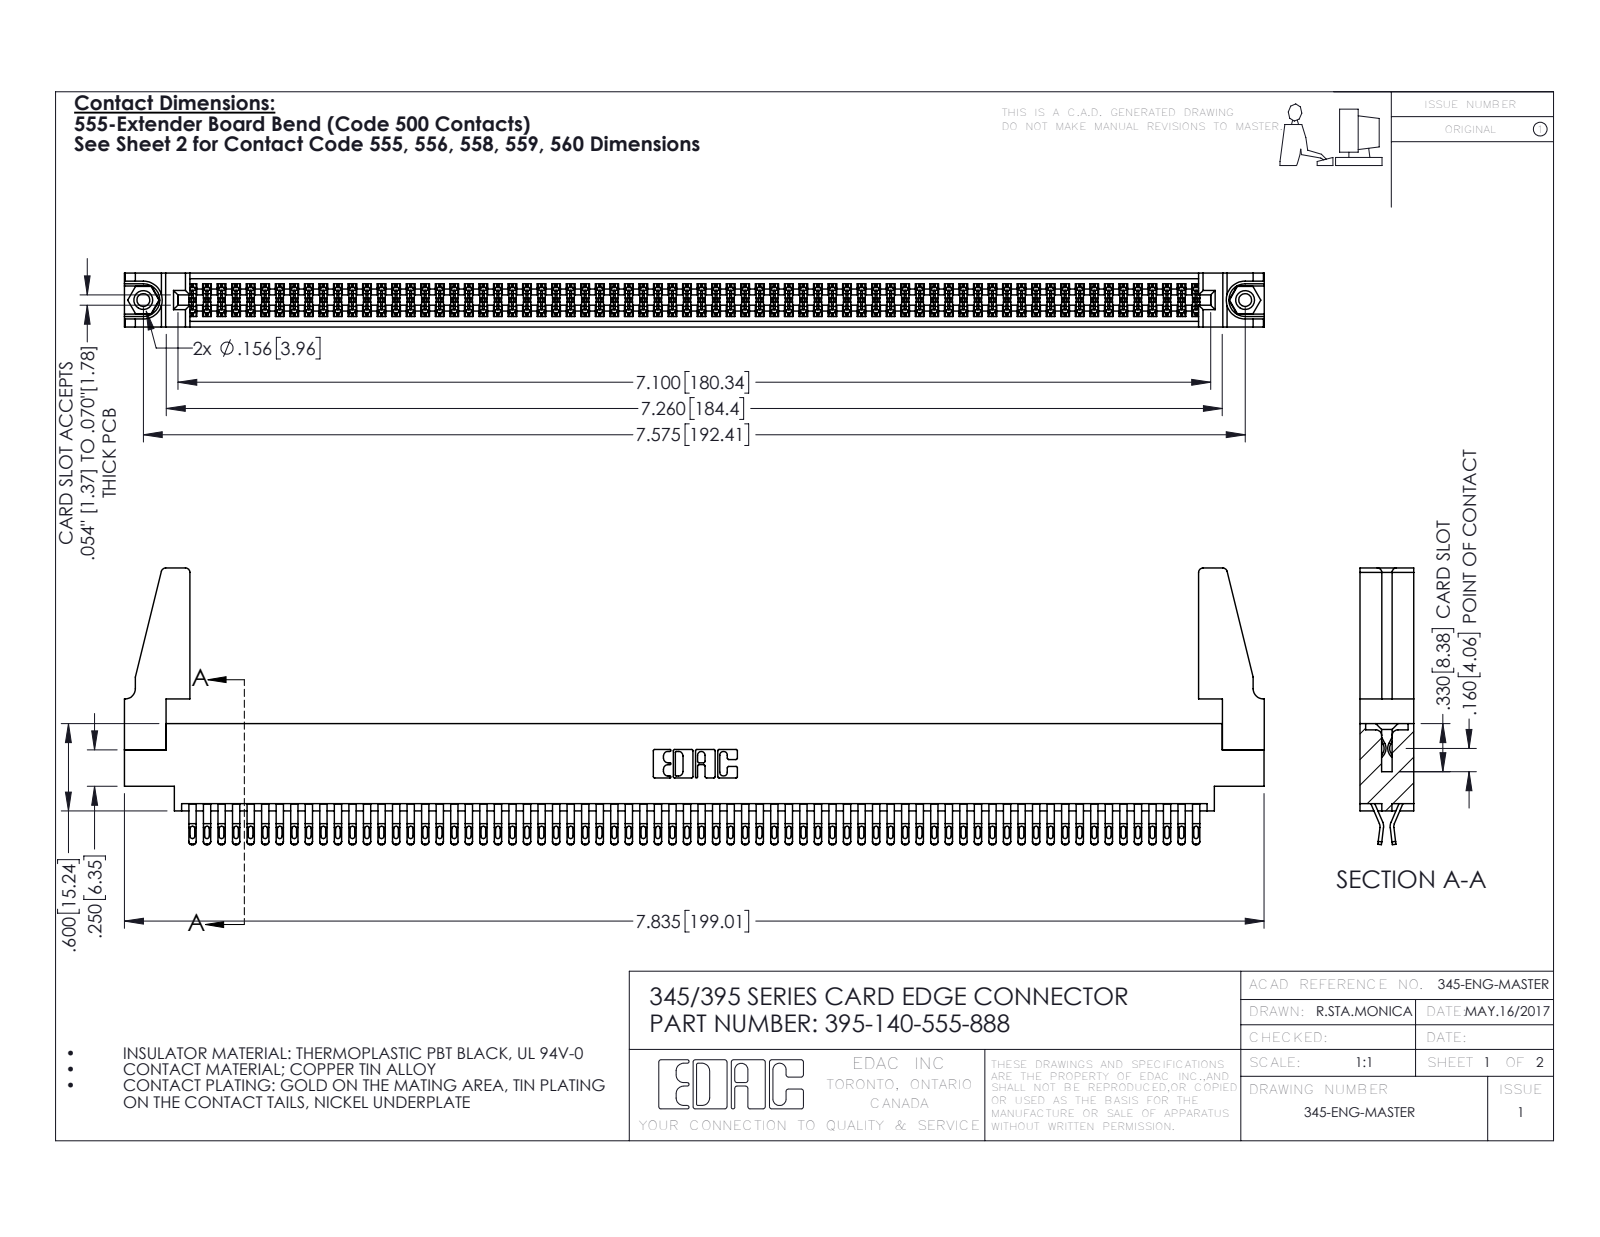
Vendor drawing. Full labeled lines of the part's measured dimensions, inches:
Part name (STEP PRODUCT): 345-220-078_345-220-088; 345-292-001_555 Tail; 345 Part_0.170 Offset - 0.156 Dia-TH; 395-140-555-888 (+1 more)
STEP written by: SolidWorks 2016 (CONFIG_CONTROL_DESIGN)
Units: inches
Bodies: 145 solids, 8094 faces (4496 planar, 3582 cylindrical, 16 other)
Overall size (bounding box): 7.836 × 1.902 × 0.37
Volume: 1.412 in³ · Surface area: 53.66 in²
Round holes (diameter × count): ⌀0.089 ×2, ⌀0.125 ×2, ⌀0.156 ×2, ⌀0.064 ×1
Round bosses / shafts (diameter × count): ⌀0.155 ×2
Partial cylindrical surfaces — rounded edges, fillets, slot ends (radius × count): R0.016 ×350, R0.02 ×280, R0.006 ×210, R0.01 ×22, R0.03 ×8, R0.007 ×6, R0.031 ×6, R0.026 ×3
Main face-to-face distances: 0.072, 0.298, 0.37, 0.025, 0.2, 0.098, 0.272, 0.225, 0.175, 0.149
Hole centre spacings: 0.27, 7.339, 7.575
